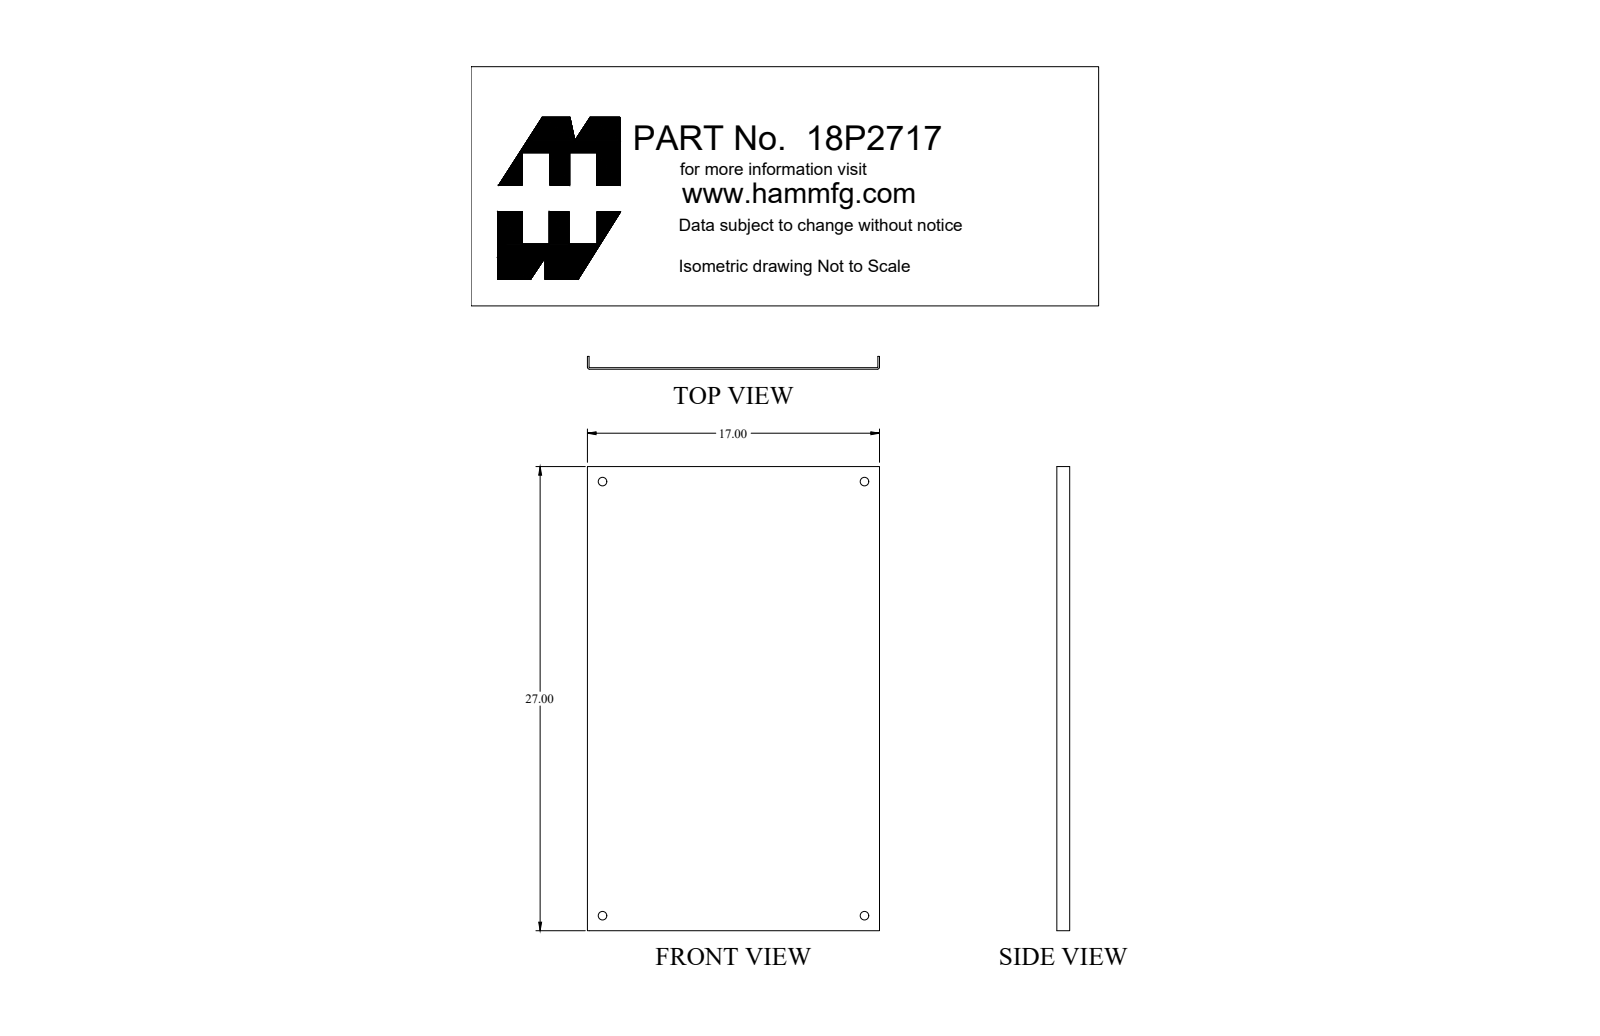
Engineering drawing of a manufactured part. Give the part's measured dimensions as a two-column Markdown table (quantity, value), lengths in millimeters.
| quantity | value |
| --- | --- |
| part name | 18P2717_Default |
| STEP written by | SolidWorks 2018 (CONFIG_CONTROL_DESIGN) |
| units | millimeters |
| bodies | 1 solid, 22 faces (10 planar, 12 cylindrical, 0 other) |
| overall size | 685.8 × 431.8 × 19.1 |
| volume | 765 600 mm³ |
| surface area | 640 500 mm² |
| round holes (diameter × count) | 12.7 × 4 |
| partial cylindrical surfaces (radius × count) | 0.8 × 2, 3.2 × 2 |
| main face-to-face distances | 2.4, 429.4, 431.8, 427, 19.1, 16.6, 685.8 |
| hole center spacings | 387.4, 641.4, 749.2 |
